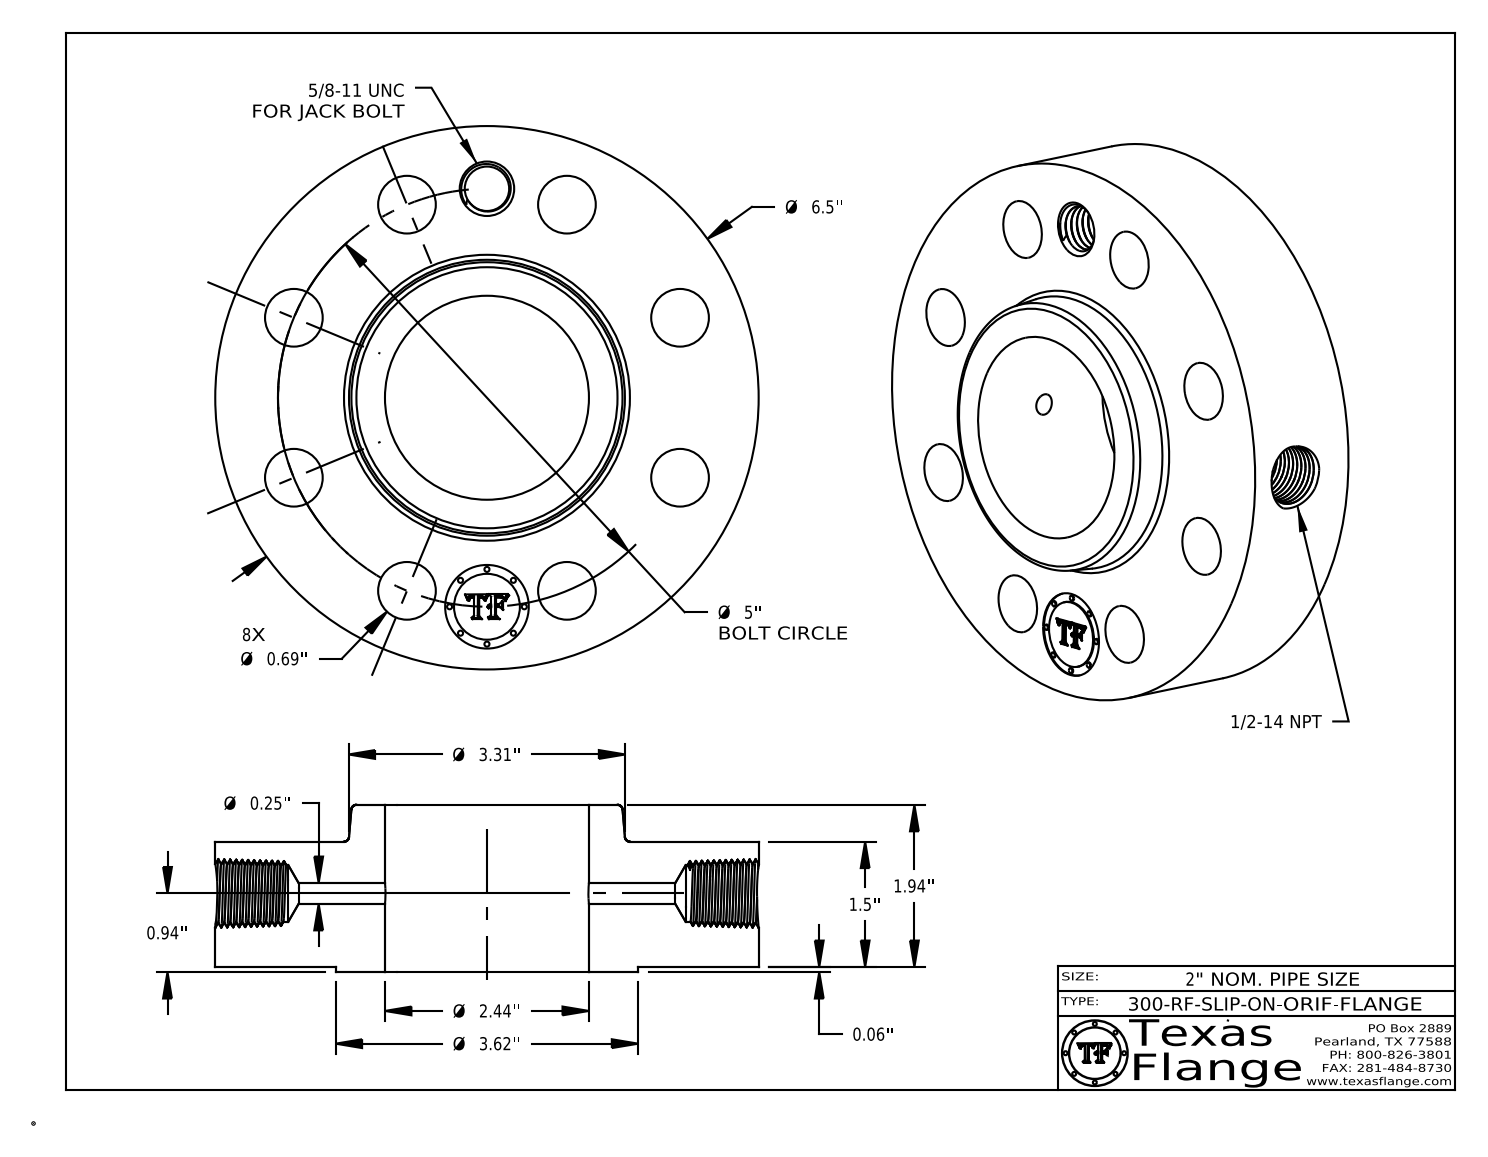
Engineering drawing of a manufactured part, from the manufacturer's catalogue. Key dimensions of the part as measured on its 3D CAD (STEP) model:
Part name (STEP PRODUCT): 300-RF-SLIP-ON
STEP written by: CATIA V5 STEP AP214 (AUTOMOTIVE_DESIGN)
Units: inches
Bodies: 1 solid, 776 faces (369 planar, 93 cylindrical, 314 other)
Overall size (bounding box): 6.5 × 6.5 × 2
Volume: 38.97 in³ · Surface area: 139.4 in²
Round holes (diameter × count): ⌀0.69 ×8, ⌀0.25 ×1, ⌀0.531 ×1, ⌀0.672 ×1, ⌀1 ×1, ⌀2.44 ×1
Round bosses / shafts (diameter × count): ⌀0.061 ×8, ⌀6.5 ×1, ⌀3.62 ×1, ⌀0.788 ×1
Main face-to-face distances: 1.5, 0.06, 1.56, 2, 1.94, 0.44, 1.545, 1.485, 0.015, 0.455
Hole centre spacings: 2.5, 3.536, 4.62, 0.976, 1.913, 1.914, 2.778, 4.157
